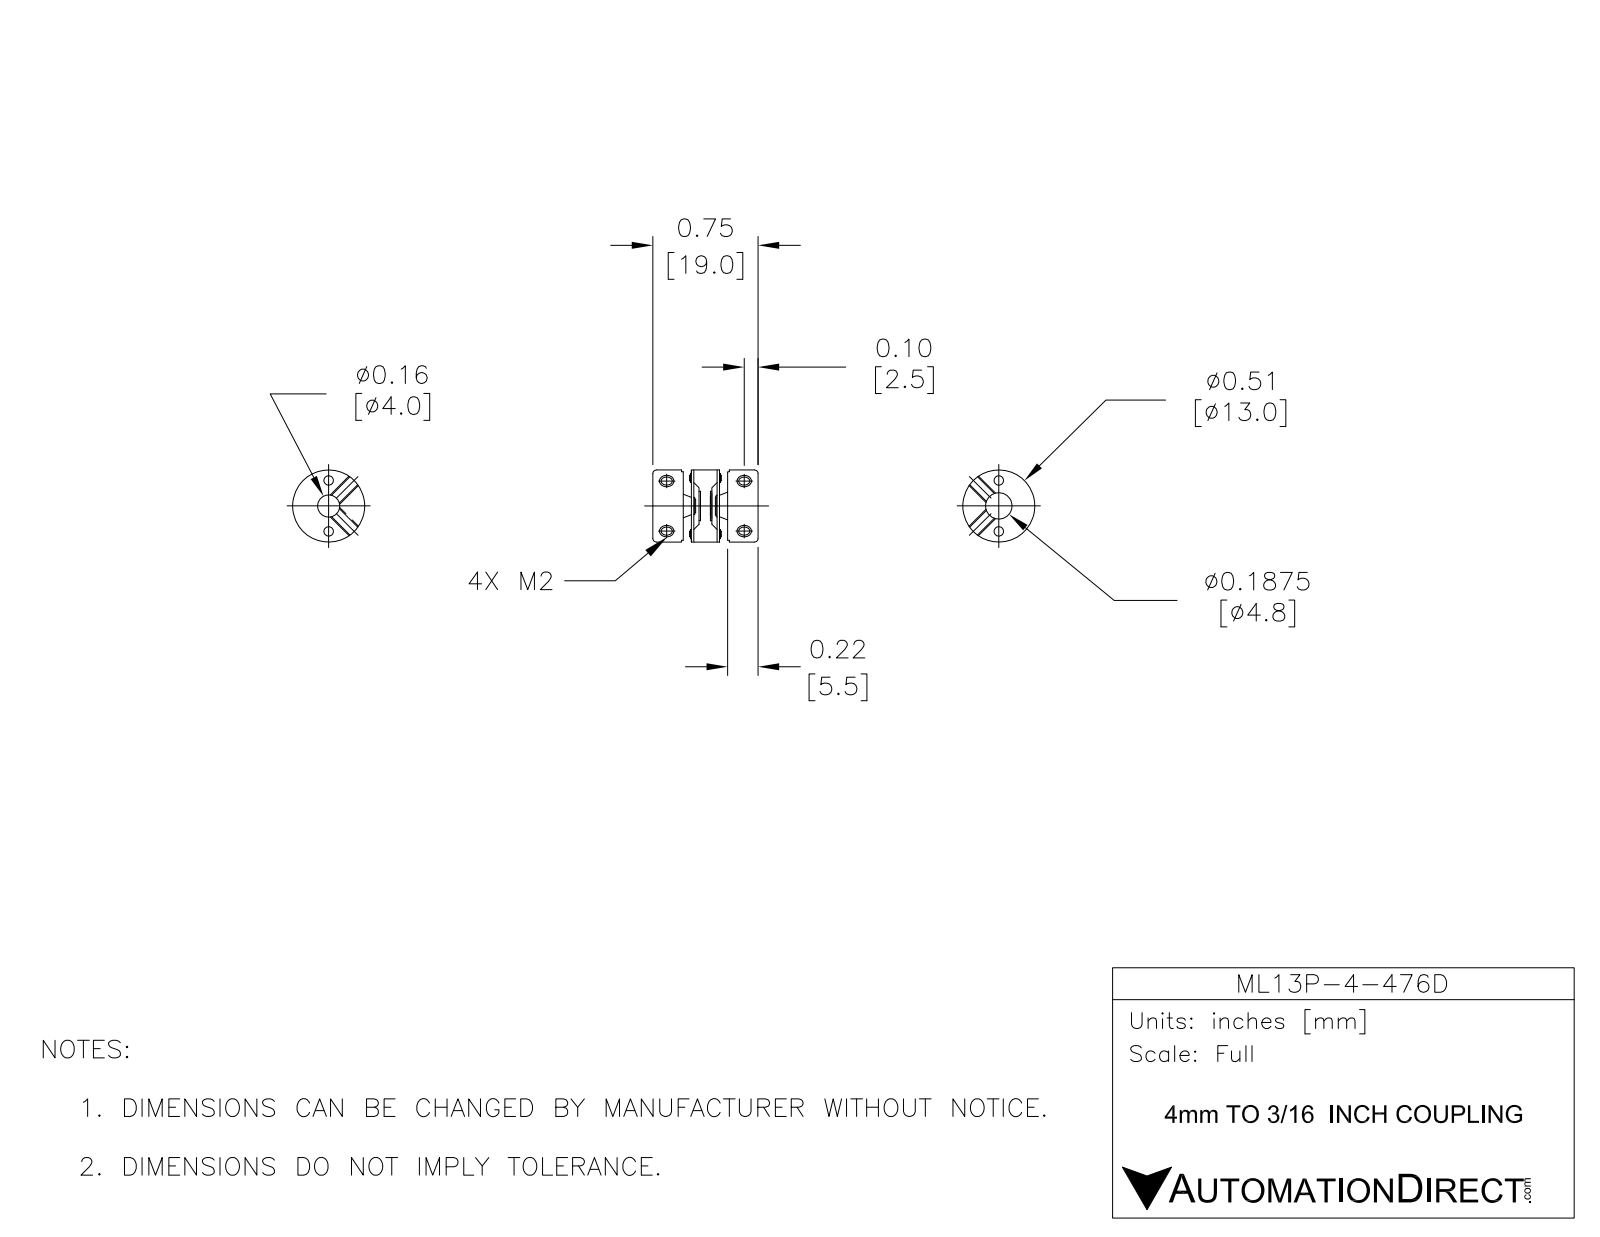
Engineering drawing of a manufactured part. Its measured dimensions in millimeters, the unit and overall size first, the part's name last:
Units: millimetres
Overall size (bounding box): 19 × 13 × 13
Round holes (diameter × count): ⌀2 ×4, ⌀1.8 ×2, ⌀4 ×1, ⌀4.76 ×1, ⌀5.3 ×1, ⌀6 ×1
Round bosses / shafts (diameter × count): ⌀13 ×1
Main face-to-face distances: 5.5, 7, 6.5, 1, 1.5, 8, 12, 12.5, 0.5, 13.5
Hole centre spacings: 4.7, 14, 9.4
Volume: 1 738 mm³ · Surface area: 2 031 mm²
Bodies: 1 solid, 158 faces (86 planar, 36 cylindrical, 36 other)
Part name (STEP PRODUCT): ML13P-4-476D
STEP written by: SolidWorks 2016 (AUTOMOTIVE_DESIGN)
